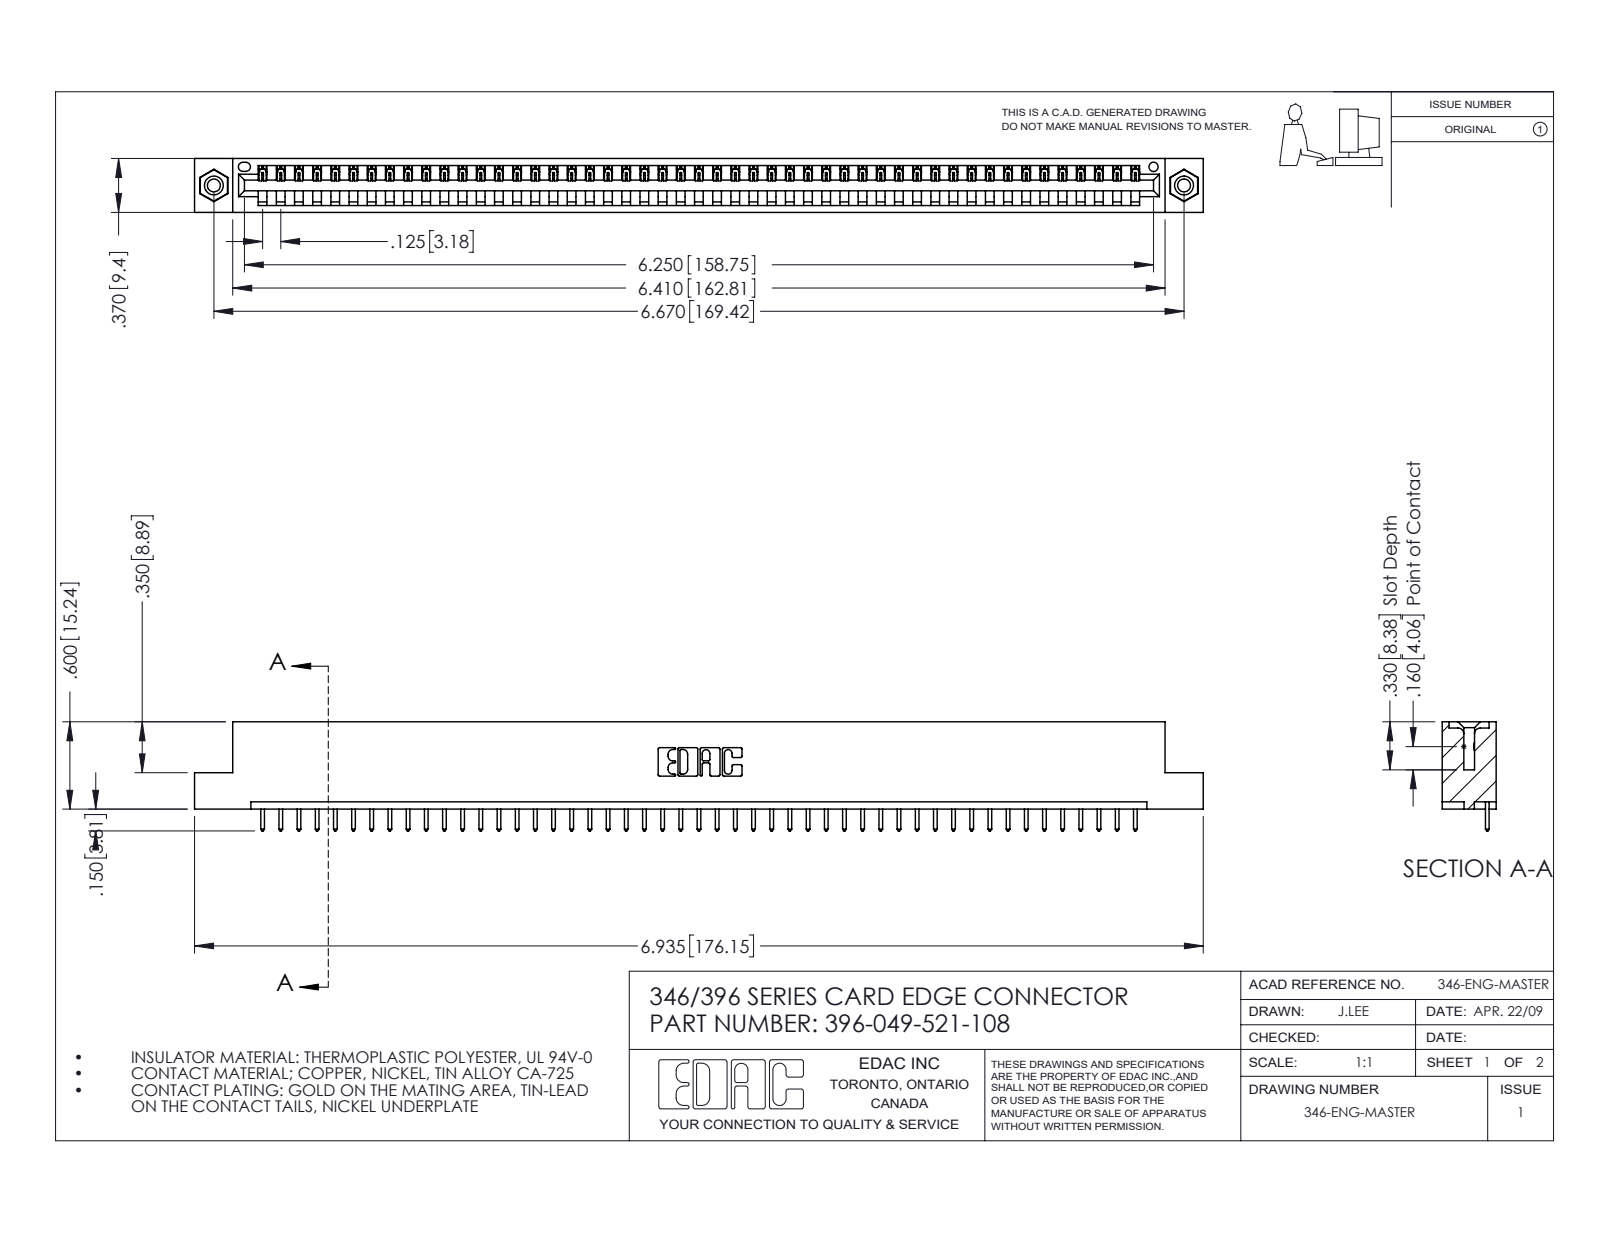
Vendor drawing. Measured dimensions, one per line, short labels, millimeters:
name: 345-250-001_345-250-003-102; 396-049-521-108; 346 Part_Flush Mounting Lugs - 0.156 Dia-TI; 345-292-001_345-293-121
written by: SolidWorks 2016 (CONFIG_CONTROL_DESIGN)
unit: mm
bodies: 52 solids, 3024 faces (2068 planar, 940 cylindrical, 16 other)
size: 176.1 × 19.1 × 9.4
volume: 16 760 mm³; area: 20 500 mm²
holes: 2× ⌀2.3, 2× ⌀3.2, 2× ⌀4, 1× ⌀1.6
bosses: 2× ⌀3.9
rounds: 98× R0.2, 98× R0.3, 22× R0.3, 6× R0.2, 6× R0.8, 3× R0.7, 2× R0.8, 2× R1
face distances: 1.2, 8.2, 9.4, 6.4, 1.8, 7.6, 0.6, 3.8, 5.6, 2.5
hole spacings: 6.2, 164.1, 169.4
